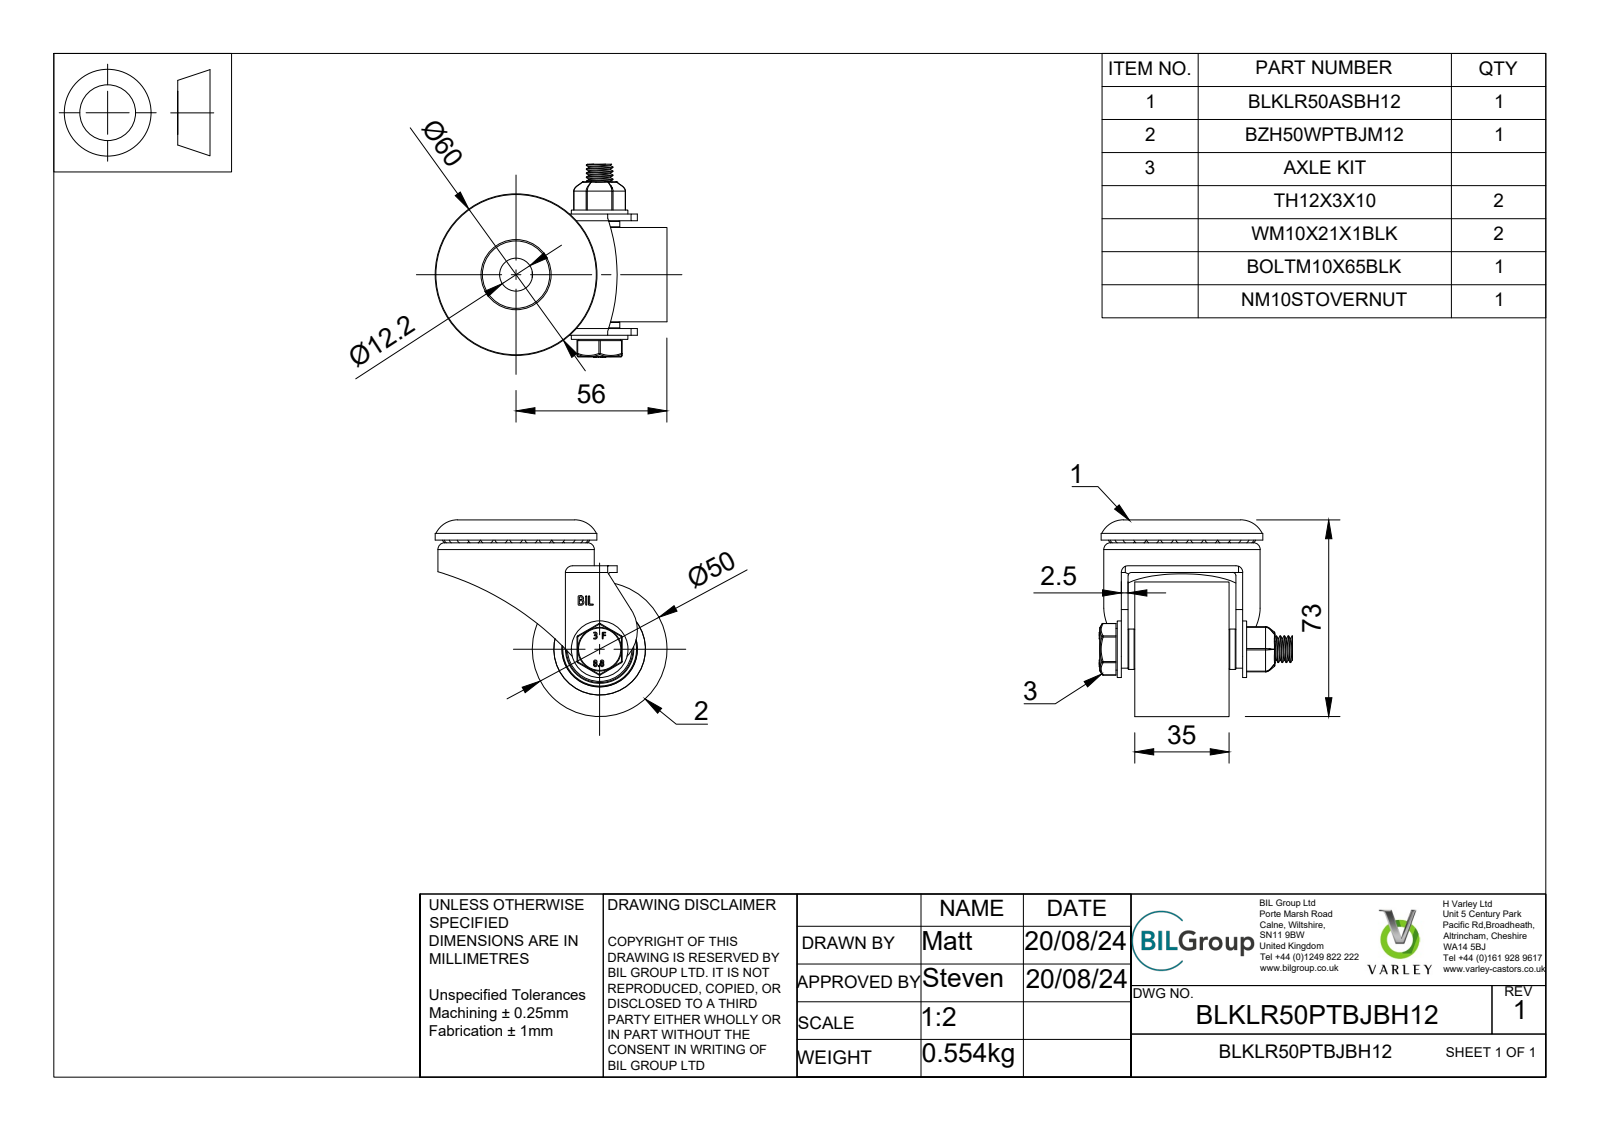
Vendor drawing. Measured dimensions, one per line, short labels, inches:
name: BLKLR50PTBJBH12 v3; BLKLR50ASBH12 v1; BLACK PAINTED PRESSED STEEL HEAD; BLACK PAINTED PRESSED STEEL HEAD Geometry (+7 more)
written by: Autodesk Translation Framework v13.14.0.145 (AUTOMOTIVE_DESIGN)
unit: in
bodies: 64 solids, 699 faces (171 planar, 212 cylindrical, 316 other)
size: 3.386 × 2.874 × 2.823
volume: 5.767 in³; area: 103.9 in²
holes: 1× ⌀0.394, 1× ⌀0.402, 1× ⌀0.413, 1× ⌀0.472, 1× ⌀0.48, 1× ⌀0.669, 1× ⌀0.689, 1× ⌀0.699, 1× ⌀0.973, 1× ⌀1.004, 1× ⌀1.101, 1× ⌀1.339
bosses: 2× ⌀1.102, 1× ⌀2.362, 1× ⌀2.008, 1× ⌀1.969, 1× ⌀0.984, 1× ⌀0.866, 1× ⌀0.827, 1× ⌀0.709
rounds: 12× R0.02, 4× R0.013, 4× R0.025, 4× R0.049, 3× R0.006, 3× R0.025, 3× R0.191, 2× R0.013
face distances: 0.098, 1.575, 0.197, 1.378, 1.673, 1.476, 0.157, 0.335, 0.059, 0.315
